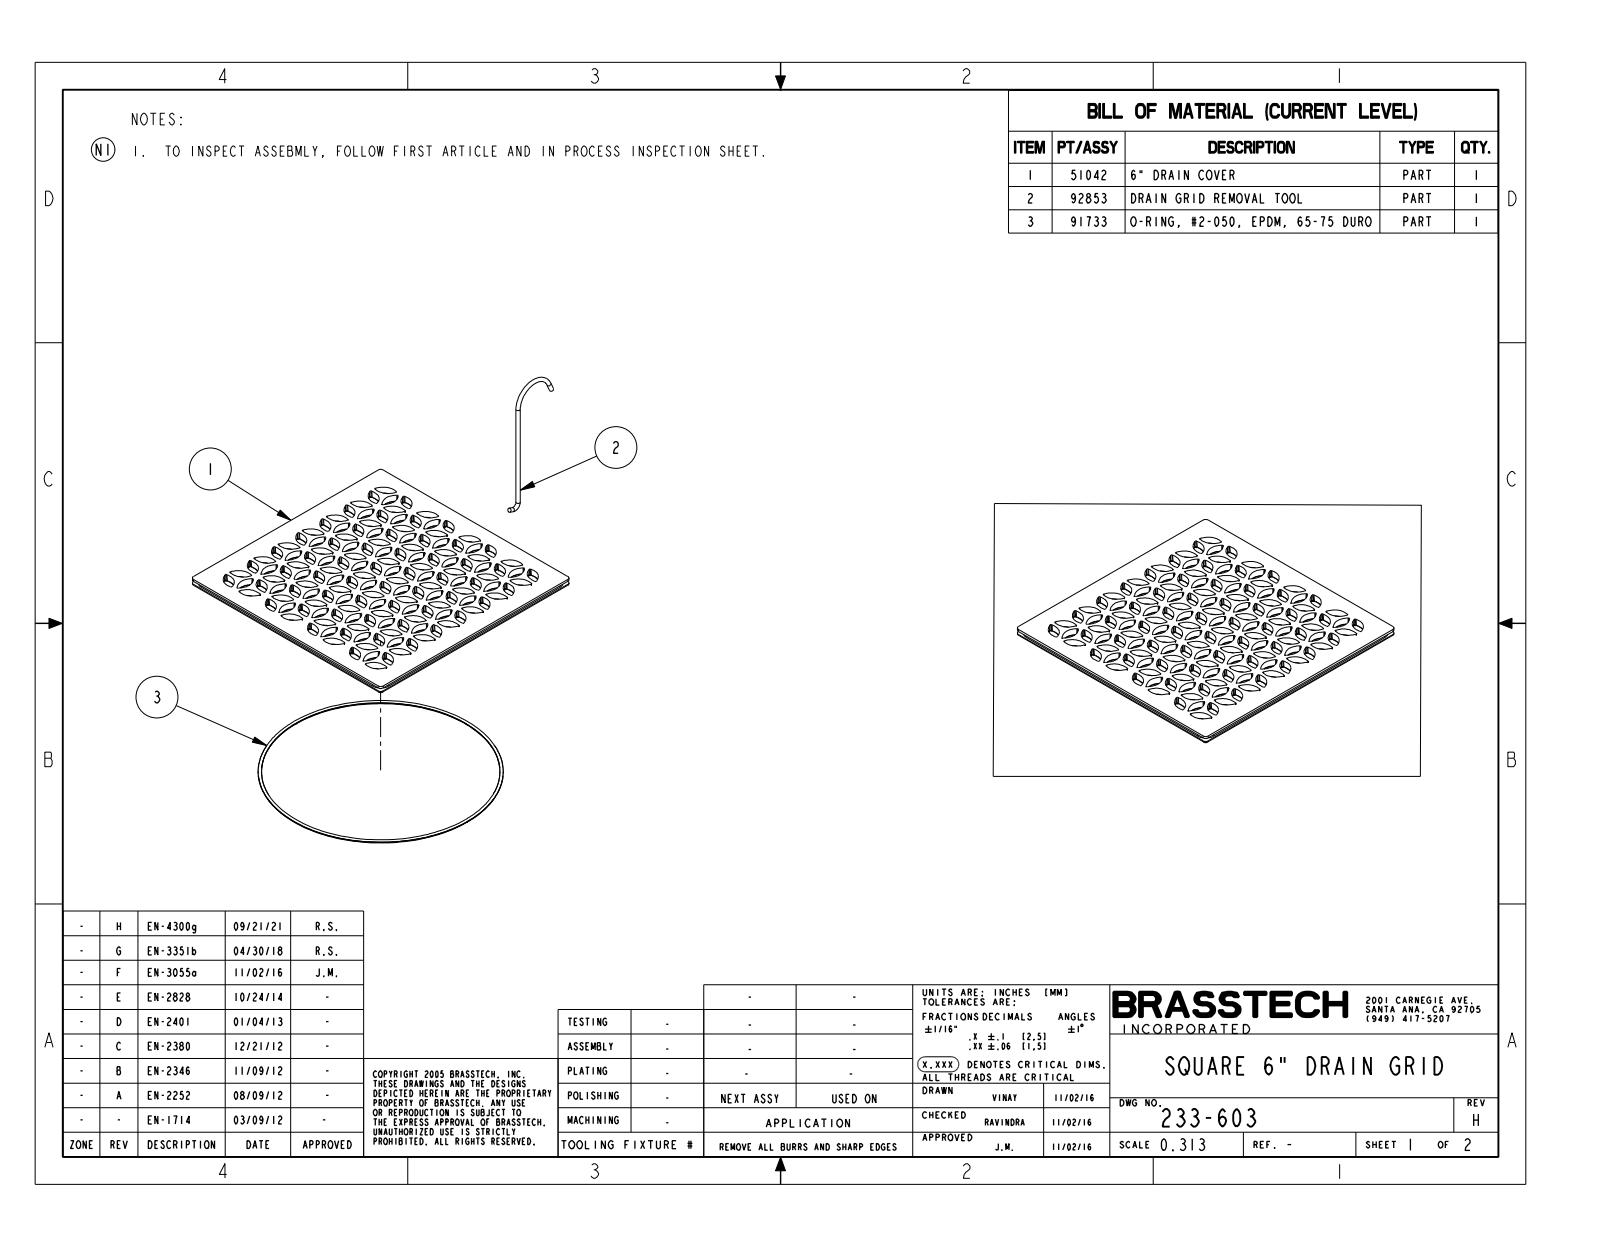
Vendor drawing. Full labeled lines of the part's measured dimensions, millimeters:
Part name (STEP PRODUCT): 51042
STEP written by: CREO PARAMETRIC BY PTC INC, 2018400 (AUTOMOTIVE_DESIGN)
Units: millimetres
Bodies: 1 solid, 2560 faces (652 planar, 958 cylindrical, 950 other)
Overall size (bounding box): 149.7 × 149.7 × 4.8
Volume: 61 930 mm³ · Surface area: 52 610 mm²
Partial cylindrical surfaces — rounded edges, fillets, slot ends (radius × count): R0.5 ×946, R2 ×4, R6.4 ×4
Main face-to-face distances: 4.8, 1.1, 148.7, 3.4, 1.4, 1.4, 2, 3.4, 149.7, 147.6
